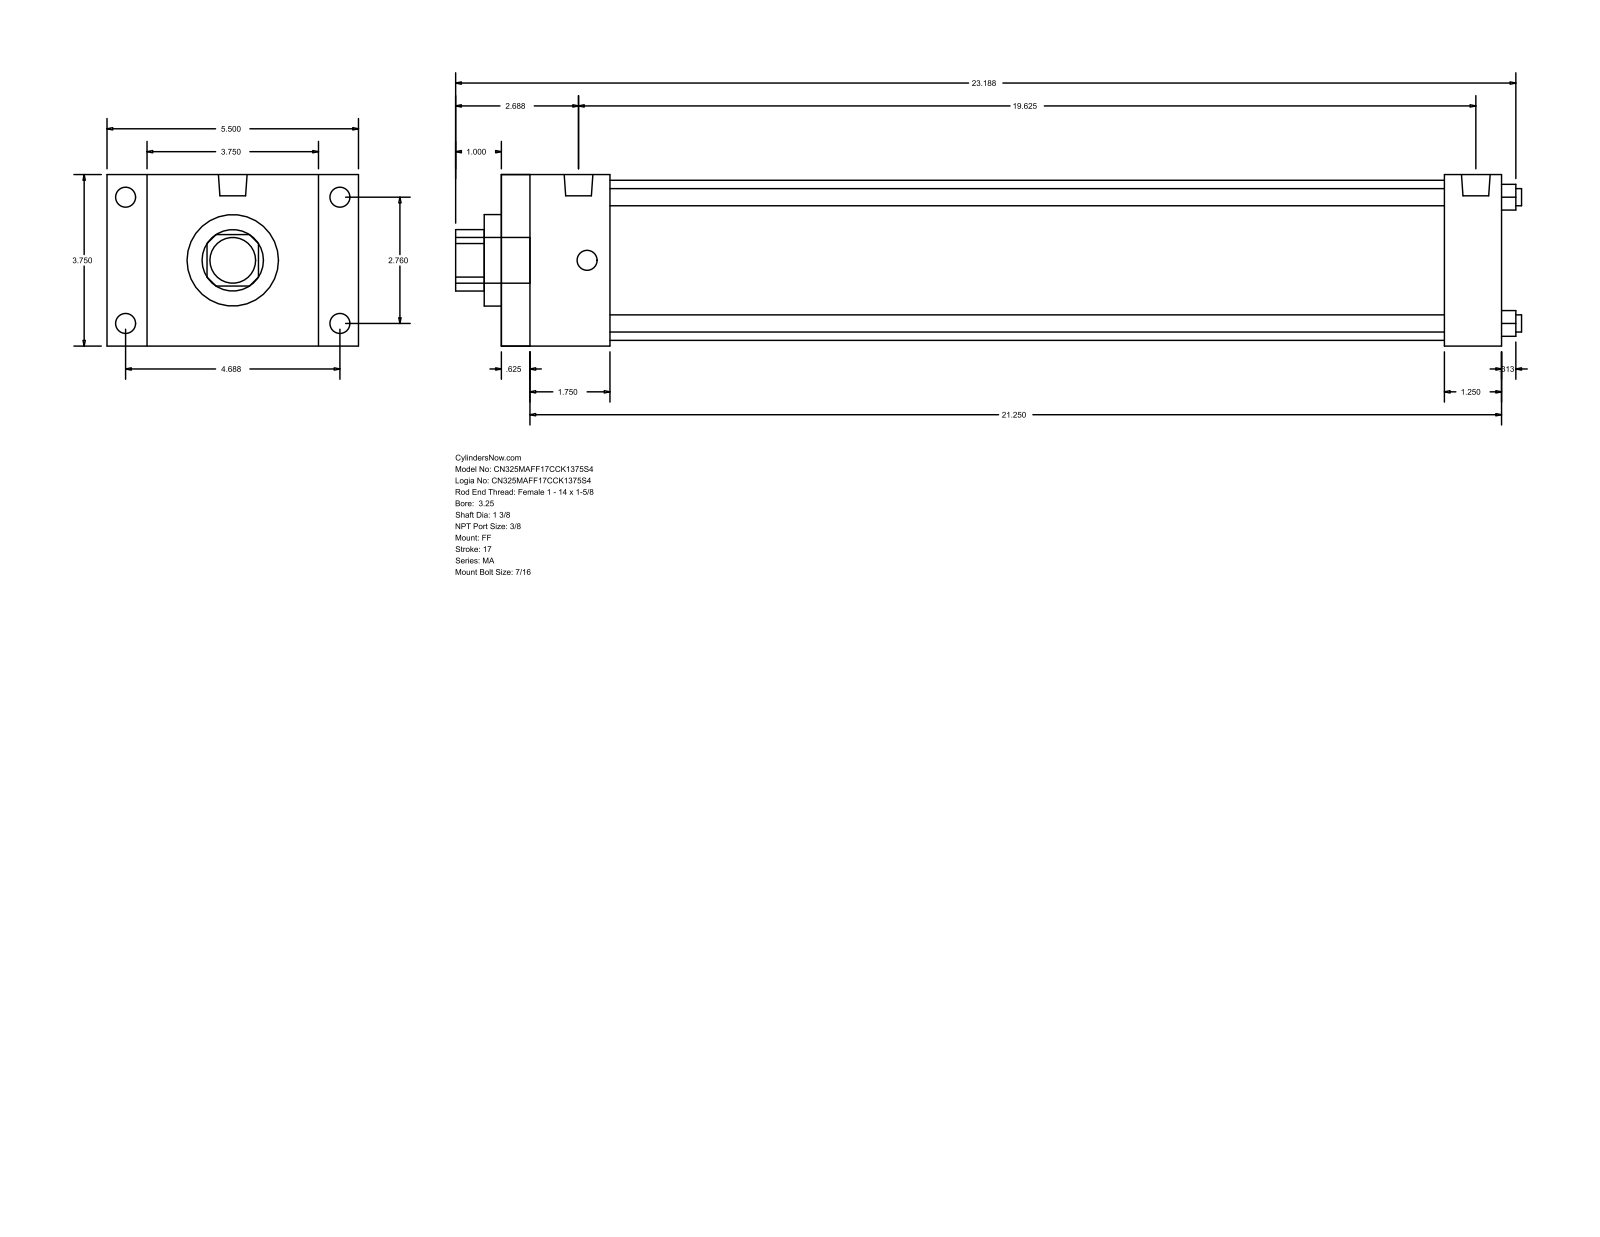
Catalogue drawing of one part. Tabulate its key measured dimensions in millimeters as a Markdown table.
| quantity | value |
| --- | --- |
| part name | MA_FF__0325_1.375 |
| STEP written by | GSSL Pune (CONFIG_CONTROL_DESIGN) |
| units | millimeters |
| bodies | 0 solids, 92 faces (64 planar, 28 cylindrical, 0 other) |
| overall size | 592.14 × 139.7 × 95.25 |
| round holes (diameter × count) | 9.53 × 4, 34.92 × 1, 50.8 × 1, 88.9 × 1 |
| round bosses / shafts (diameter × count) | 11.11 × 8, 15.93 × 2, 25.4 × 1 |
| partial cylindrical surfaces (radius × count) | 17.06 × 1 |
| main face-to-face distances | 95.24, 555.62, 15.87, 539.75, 22.23, 117.47, 60.32, 523.87, 44.45, 508 |
| hole center spacings | 49.57, 70.1, 99.14 |
